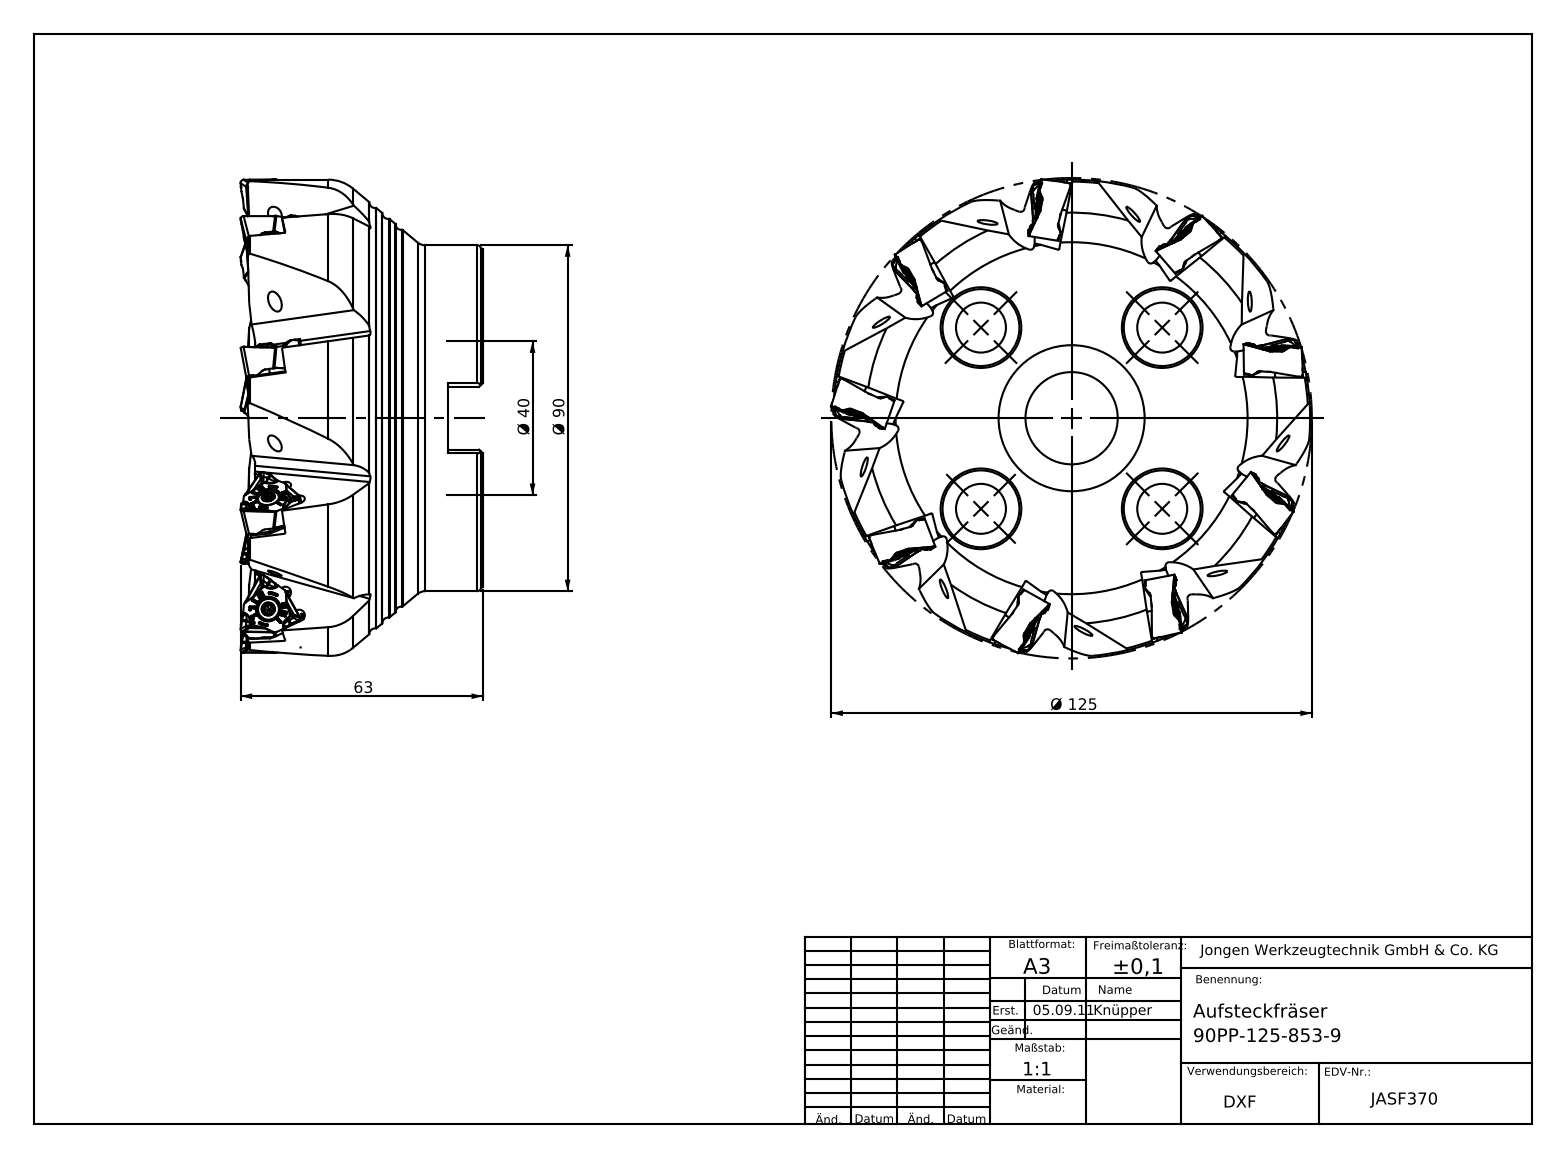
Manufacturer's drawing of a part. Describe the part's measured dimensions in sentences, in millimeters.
The part is named "90PP-125-853-9". Its 3-D file was written by "SolidWorks 2010 (AUTOMOTIVE_DESIGN)". It is 1 solid with 498 faces: 135 planar, 191 cylindrical and 172 other. Overall it measures 125 by 125 by 63 millimeters. Its volume is 447 609 cubic millimeters and its surface area 65 679 square millimeters. Round holes: 4 of diameter 13, 4 of diameter 20, 1 of diameter 24, 1 of diameter 40, 1 of diameter 40.15, 1 of diameter 40.3. Round bosses or shafts: 1 of diameter 125, 1 of diameter 124.15, 1 of diameter 90. Partial cylindrical surfaces (rounded edges, fillets, slot ends): 63 of radius 0.3, 18 of radius 1.5, 9 of radius 1, 9 of radius 10. The main face-to-face distances are 59.25, 61.2, 1.95, 9, 50.25, 52.2, 31, 22, 28.25, 30.2. The hole center spacings are 33.35, 47.16, 66.69.
